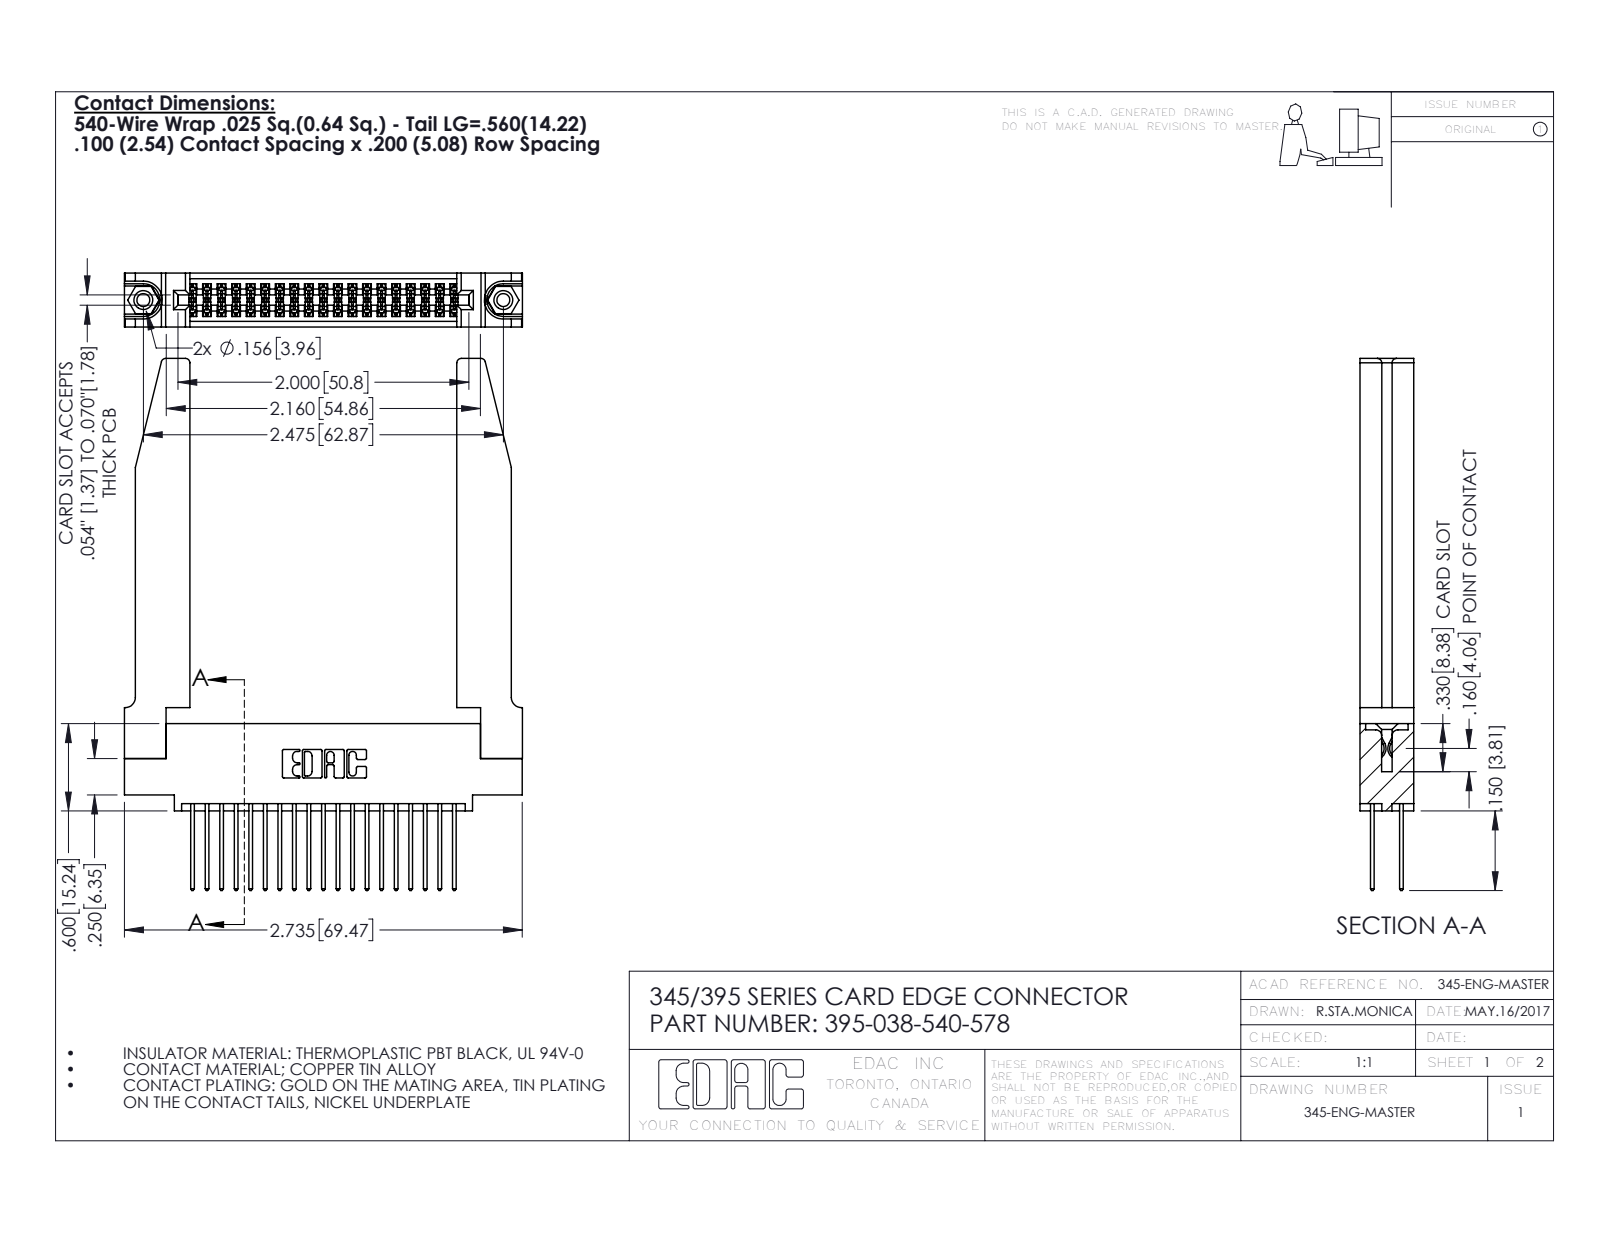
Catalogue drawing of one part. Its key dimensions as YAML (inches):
part_name: "345-220-078_345-220-078; 345 Part_0.110 Offset - 0.156 Dia-TH; 395-038-540-578; 345-292-001_345-293-140 (+1 more)"
step_written_by: "SolidWorks 2016 (CONFIG_CONTROL_DESIGN)"
units: inches
bodies: {solids: 43, faces: 2264, planar: 1480, cylindrical: 732, other: 52}
overall_size: [3.657, 2.736, 0.37]
volume: 0.877
surface_area: 26.23
round_holes:
  - {diameter: 0.089, count: 2}
  - {diameter: 0.125, count: 2}
  - {diameter: 0.156, count: 2}
  - {diameter: 0.064, count: 1}
round_bosses_or_shafts:
  - {diameter: 0.155, count: 2}
partial_cylinders:
  - {radius: 0.006, count: 57}
  - {radius: 0.01, count: 38}
  - {radius: 0.01, count: 22}
  - {radius: 0.03, count: 8}
  - {radius: 0.007, count: 6}
  - {radius: 0.031, count: 6}
  - {radius: 0.026, count: 3}
  - {radius: 0.014, count: 2}
face_to_face_distances: [0.37, 0.072, 0.298, 0.2, 0.098, 0.272, 0.025, 0.225, 0.148, 0.15]
hole_center_spacings: [0.27, 2.241, 2.475]
